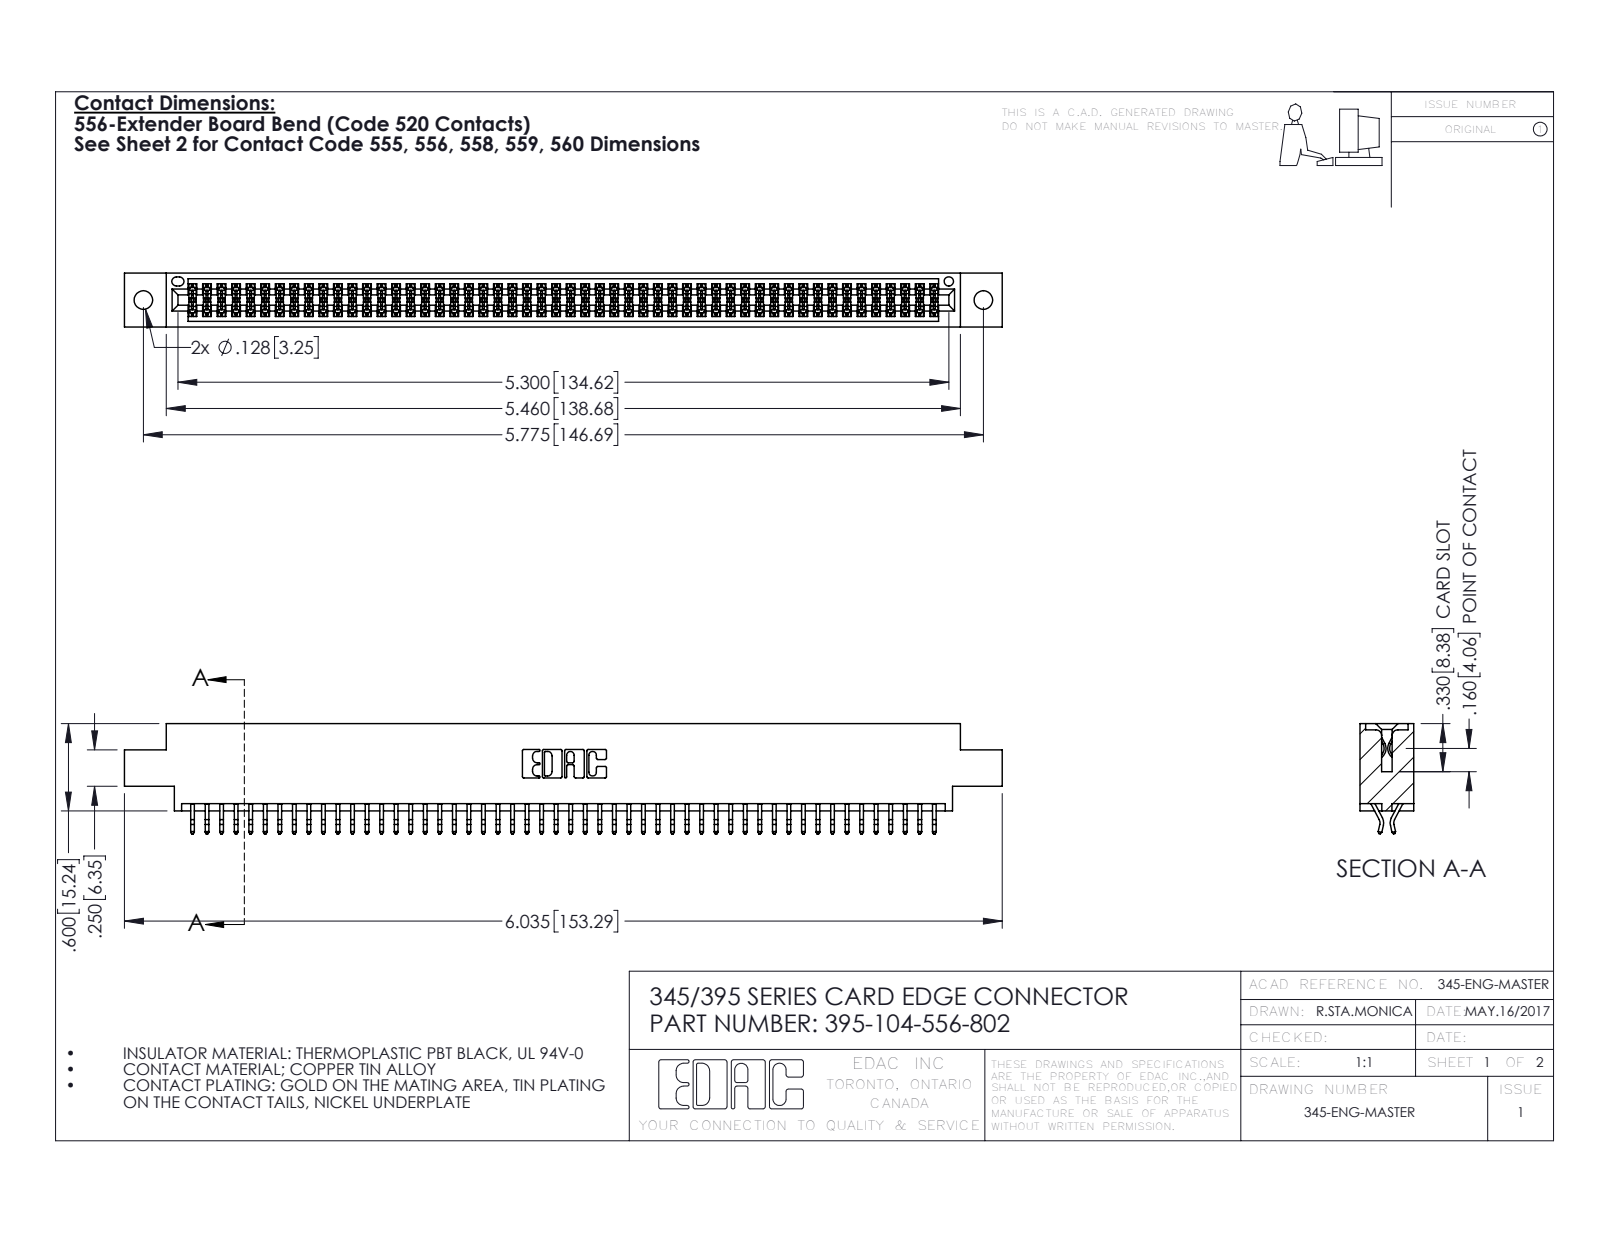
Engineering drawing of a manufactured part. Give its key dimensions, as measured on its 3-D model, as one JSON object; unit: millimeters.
{"part_name": "395-104-556-802; 345-292-001_556 Tail; 345 Part_0.170 Offset - 0.128 Dia", "step_written_by": "SolidWorks 2016 (CONFIG_CONTROL_DESIGN)", "units": "millimeters", "bodies": {"solids": 105, "faces": 5954, "planar": 3932, "cylindrical": 2022, "other": 0}, "overall_size": [153.3, 19.2, 9.4], "volume_mm3": 14800, "surface_area_mm2": 21900, "round_holes": [[3.3, 2], [1.6, 1]], "partial_cylinders_radius": [[0.2, 156], [0.3, 22], [0.2, 6], [0.8, 6], [0.7, 3], [0.3, 2], [0.4, 2], [0.5, 2]], "face_to_face_distances": [7.6, 1.8, 9.4, 5.1, 0.6, 2.5, 6.9, 5.7, 4.4, 3.8], "hole_center_spacings": [6.9, 140.7, 146.7]}
